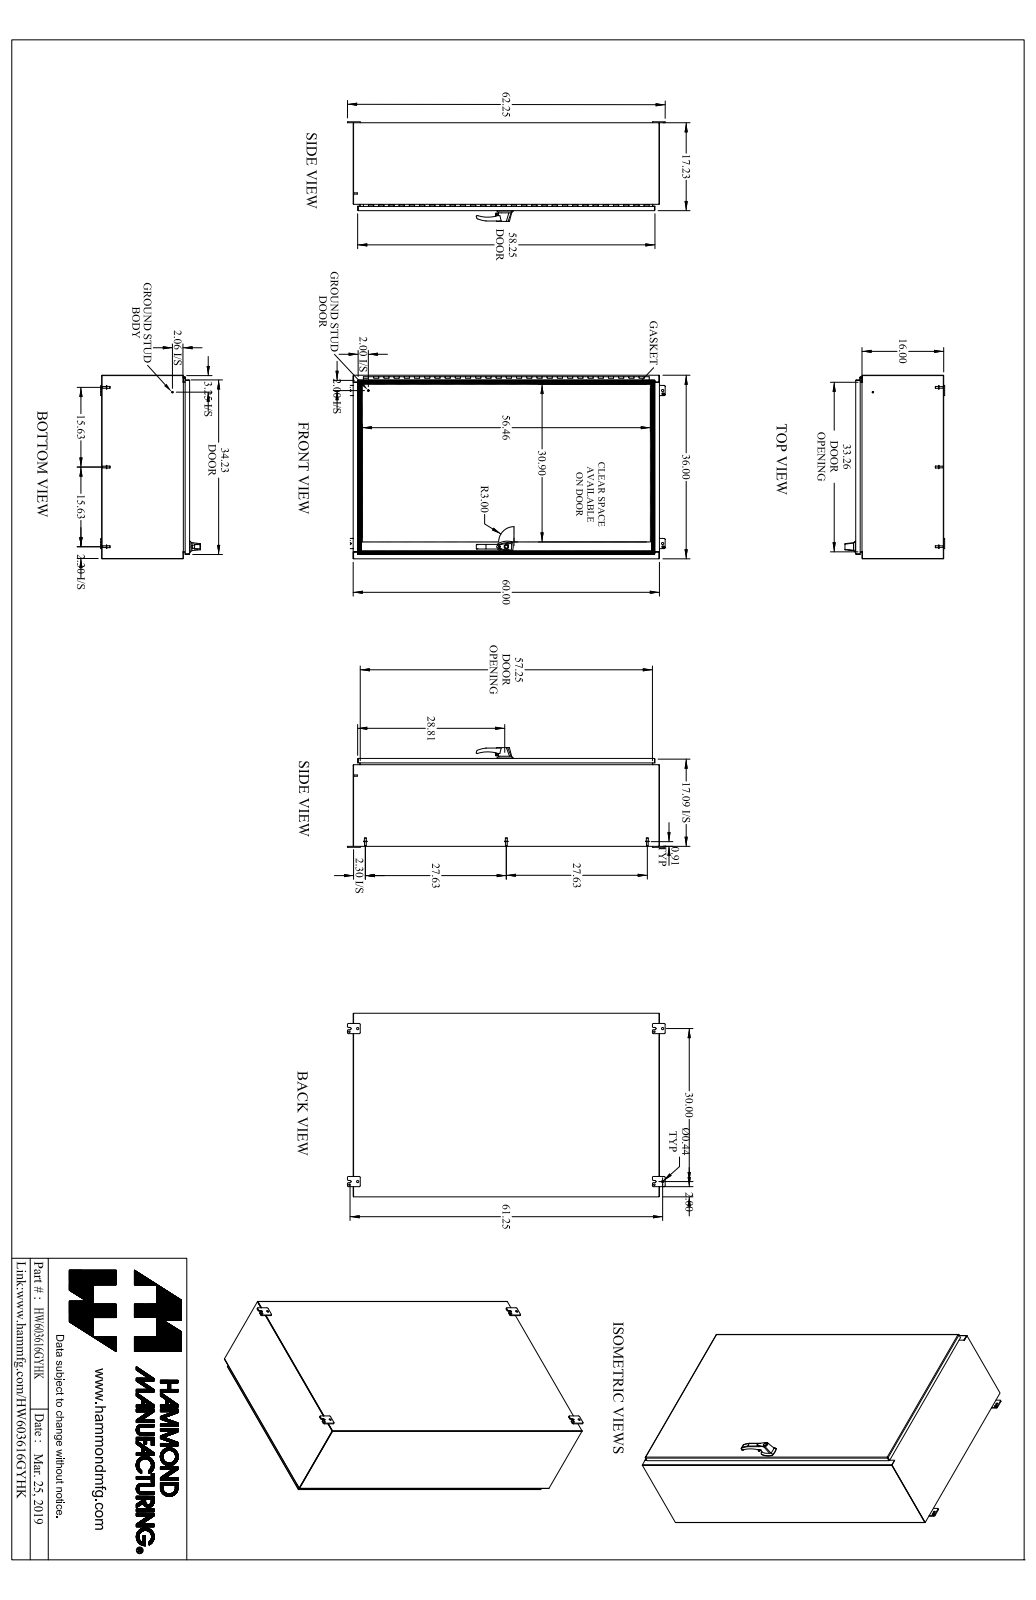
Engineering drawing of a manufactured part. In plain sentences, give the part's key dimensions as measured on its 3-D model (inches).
The part is named "HW603616GYHK". Its 3-D file was written by "SolidWorks 2018 (AUTOMOTIVE_DESIGN)". It is 49 solids with 1695 faces: 802 planar, 730 cylindrical and 163 other. Overall it measures 62.25 by 36 by 19.535 inches. Its volume is 681.6 cubic inches and its surface area 17 162 square inches. Round holes: 6 of diameter 0.176, 4 of diameter 0.25, 4 of diameter 0.313, 3 of diameter 0.196, 3 of diameter 0.265, 3 of diameter 0.413, 2 of diameter 0.256, 2 of diameter 0.394, 2 of diameter 0.437, 1 of diameter 0.187, 1 of diameter 0.233, 1 of diameter 0.334. Round bosses or shafts: 13 of diameter 0.375, 8 of diameter 0.65, 8 of diameter 0.33, 6 of diameter 0.25, 6 of diameter 0.156, 3 of diameter 1, 2 of diameter 0.63, 2 of diameter 0.51. Partial cylindrical surfaces (rounded edges, fillets, slot ends): 24 of radius 0.188, 14 of radius 0.036, 14 of radius 0.108, 12 of radius 0.116, 12 of radius 0.187, 9 of radius 0.125, 8 of radius 0.218, 7 of radius 0.06. The main face-to-face distances are 0.072, 17.138, 17.066, 0.095, 17.233, 17.161, 35.928, 59.928, 35.856, 36. The hole center spacings are 26.118, 26.119, 52.237, 1.005, 1.11, 26.119, 30, 30.659.
